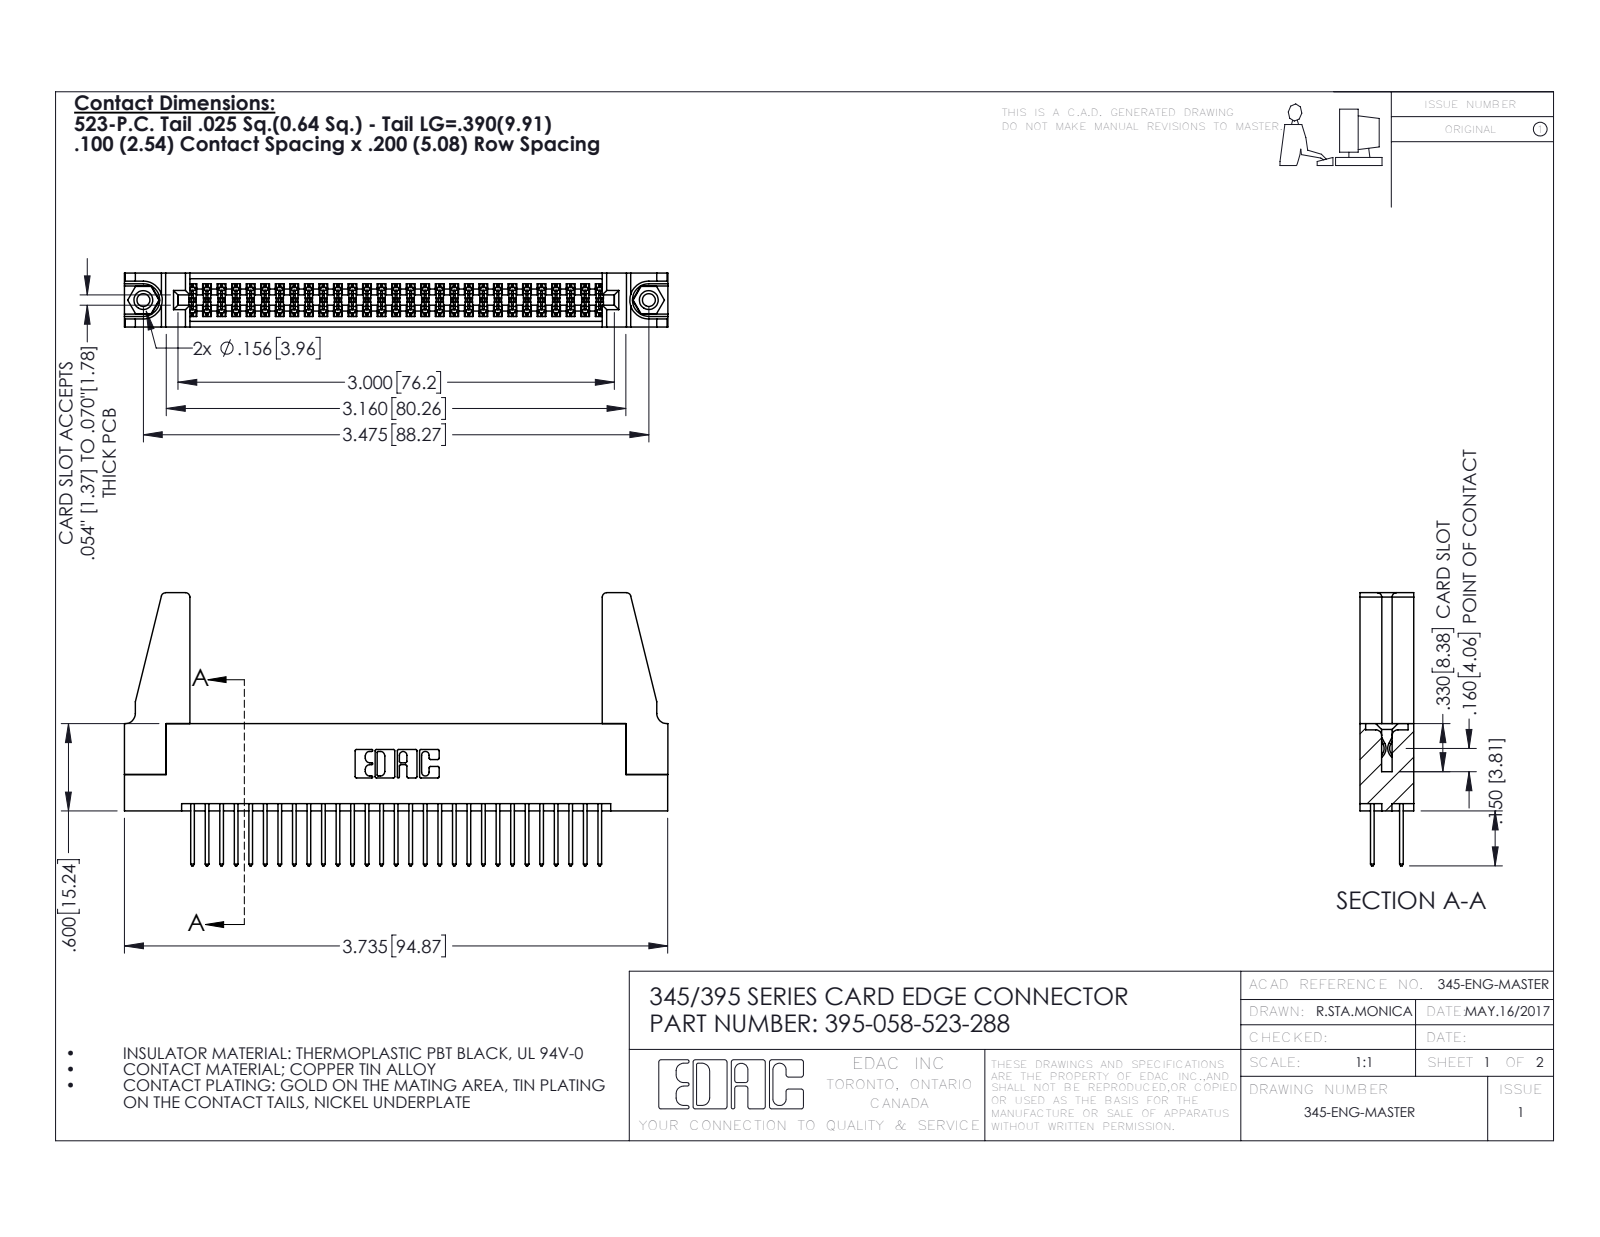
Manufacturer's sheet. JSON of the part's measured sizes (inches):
{"part_name": "345-292-001_345-293-123; 395-058-523-288; 345-250-001_345-250-001-102; 345 Part_Flush Mounting Lugs - 0.156 Dia-TH (+1 more)", "step_written_by": "SolidWorks 2016 (CONFIG_CONTROL_DESIGN)", "units": "inches", "bodies": {"solids": 63, "faces": 3150, "planar": 2066, "cylindrical": 1068, "other": 16}, "overall_size": [3.736, 1.877, 0.37], "volume_in3": 0.761, "surface_area_in2": 26.39, "round_holes": [[0.089, 2], [0.125, 2], [0.156, 2], [0.064, 1]], "round_bosses_or_shafts": [[0.155, 2]], "partial_cylinders_radius": [[0.006, 87], [0.01, 58], [0.01, 22], [0.03, 8], [0.007, 6], [0.031, 6], [0.026, 3], [0.014, 2]], "face_to_face_distances": [0.072, 0.298, 0.37, 0.2, 0.098, 0.272, 0.025, 0.225, 0.175, 0.149], "hole_center_spacings": [0.27, 3.24, 3.475]}
